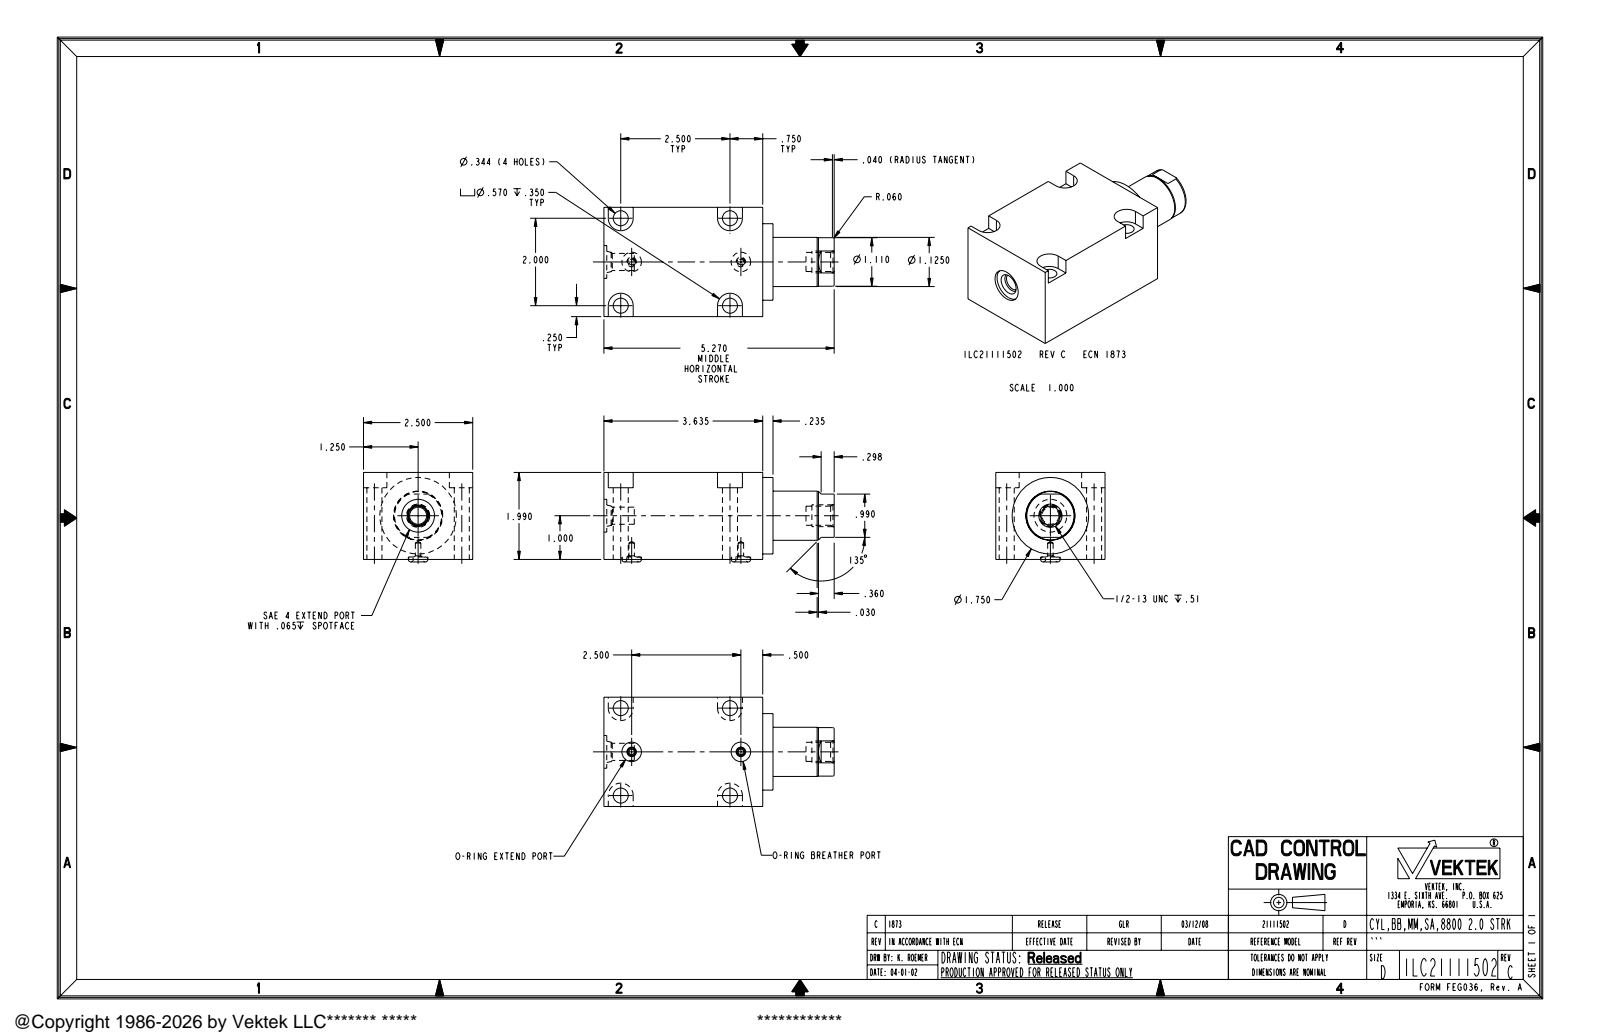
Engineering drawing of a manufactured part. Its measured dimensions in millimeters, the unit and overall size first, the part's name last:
Units: millimetres
Overall size (bounding box): 133.9 × 63.5 × 52
Round holes (diameter × count): ⌀8.7 ×4, ⌀3.2 ×2, ⌀11.4 ×2, ⌀10 ×1, ⌀11.1 ×1, ⌀19.1 ×1
Round bosses / shafts (diameter × count): ⌀44.5 ×1, ⌀28.6 ×1, ⌀28.2 ×1, ⌀12.7 ×1
Partial cylindrical surfaces — rounded edges, fillets, slot ends (radius × count): R7.2 ×4
Main face-to-face distances: 50.5, 63.5, 92.3, 6, 98.3, 41.7, 8.9, 35.6, 41.5, 133.9
Hole centre spacings: 26.2, 63.5, 50.8, 62.5, 74.3, 81.3
Volume: 308 400 mm³ · Surface area: 38 670 mm²
Bodies: 1 solid, 90 faces (30 planar, 34 cylindrical, 26 other)
Part name (STEP PRODUCT): ILC21111502
STEP written by: PRO/ENGINEER BY PARAMETRIC TECHNOLOGY CORPORATION, 2007460 (AUTOMOTIVE_DESIGN_CC2)
